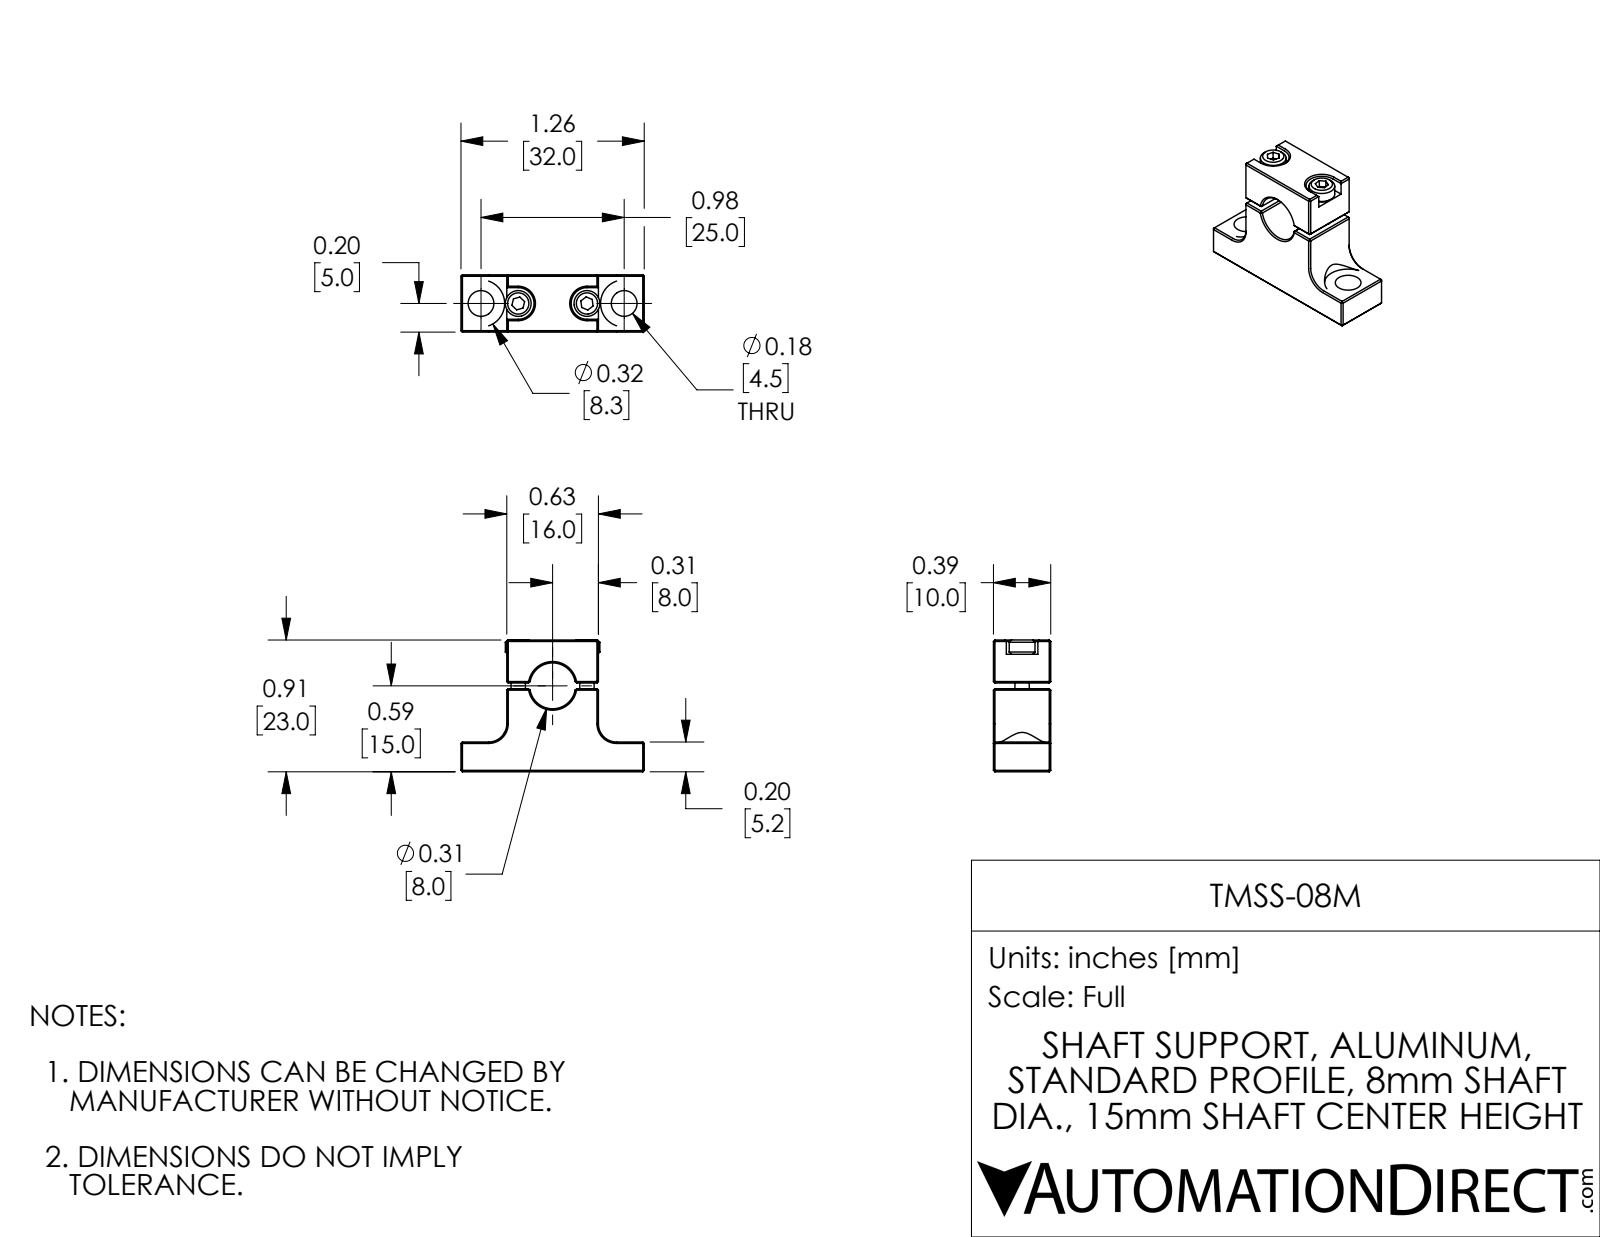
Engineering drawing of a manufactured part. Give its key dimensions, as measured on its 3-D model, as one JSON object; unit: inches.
{"part_name": "TMSS-08M", "step_written_by": "SolidWorks 2017 (AUTOMOTIVE_DESIGN)", "units": "inches", "bodies": {"solids": 4, "faces": 176, "planar": 120, "cylindrical": 32, "other": 24}, "overall_size": [1.26, 0.906, 0.394], "volume_in3": 0.224, "surface_area_in2": 4.405, "round_holes": [[0.079, 2], [0.114, 2], [0.177, 2], [0.094, 1], [0.315, 1]], "round_bosses_or_shafts": [[0.177, 2], [0.098, 2]], "partial_cylinders_radius": [[0.109, 2], [0.125, 2], [0.162, 2]], "face_to_face_distances": [0.394, 0.63, 0.906, 0.315, 0.945, 0.205, 0.701, 0.571, 0.366, 0.335], "hole_center_spacings": [0.236, 0.256, 0.492, 0.728, 0.472, 0.984]}
